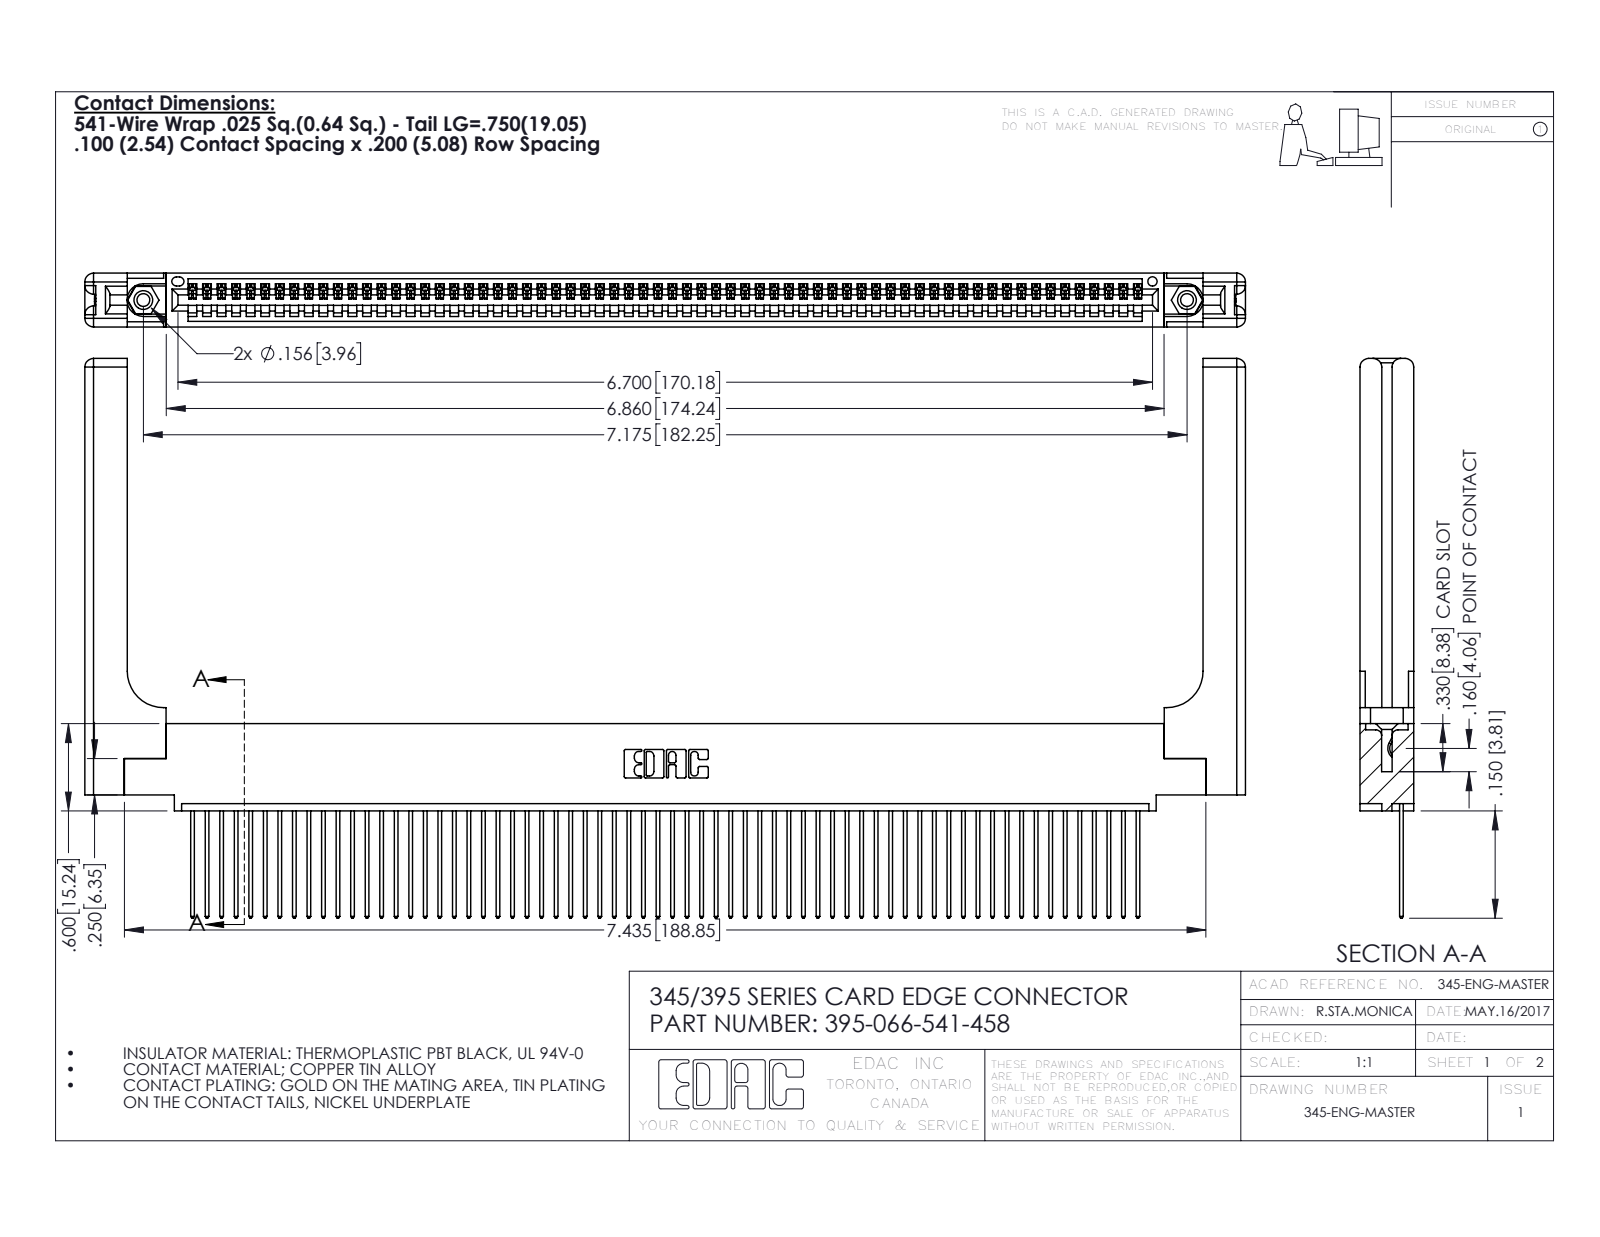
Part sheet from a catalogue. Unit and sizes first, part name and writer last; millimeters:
Units: millimetres
Overall size (bounding box): 202.7 × 97.7 × 9.4
Round holes (diameter × count): ⌀2.3 ×2, ⌀3.2 ×2, ⌀4 ×2, ⌀1.6 ×1
Round bosses / shafts (diameter × count): ⌀3.9 ×2
Partial cylindrical surfaces — rounded edges, fillets, slot ends (radius × count): R0.2 ×132, R0.3 ×132, R0.3 ×22, R1.5 ×16, R0.2 ×6, R0.8 ×6, R0.7 ×3, R0.8 ×2
Main face-to-face distances: 1.8, 7.6, 9.4, 2.5, 6.9, 0.6, 5.1, 5.7, 3.8, 3.8
Hole centre spacings: 6.9, 176.3, 182.2
Volume: 28 090 mm³ · Surface area: 33 030 mm²
Bodies: 71 solids, 4214 faces (2872 planar, 1282 cylindrical, 60 other)
Part name (STEP PRODUCT): 395-066-541-458; 345-220-058_345-220-058; 345-292-001_345-293-141; 345 Part_0.110 Offset - 0.156 Dia-TH (+1 more)
STEP written by: SolidWorks 2016 (CONFIG_CONTROL_DESIGN)
